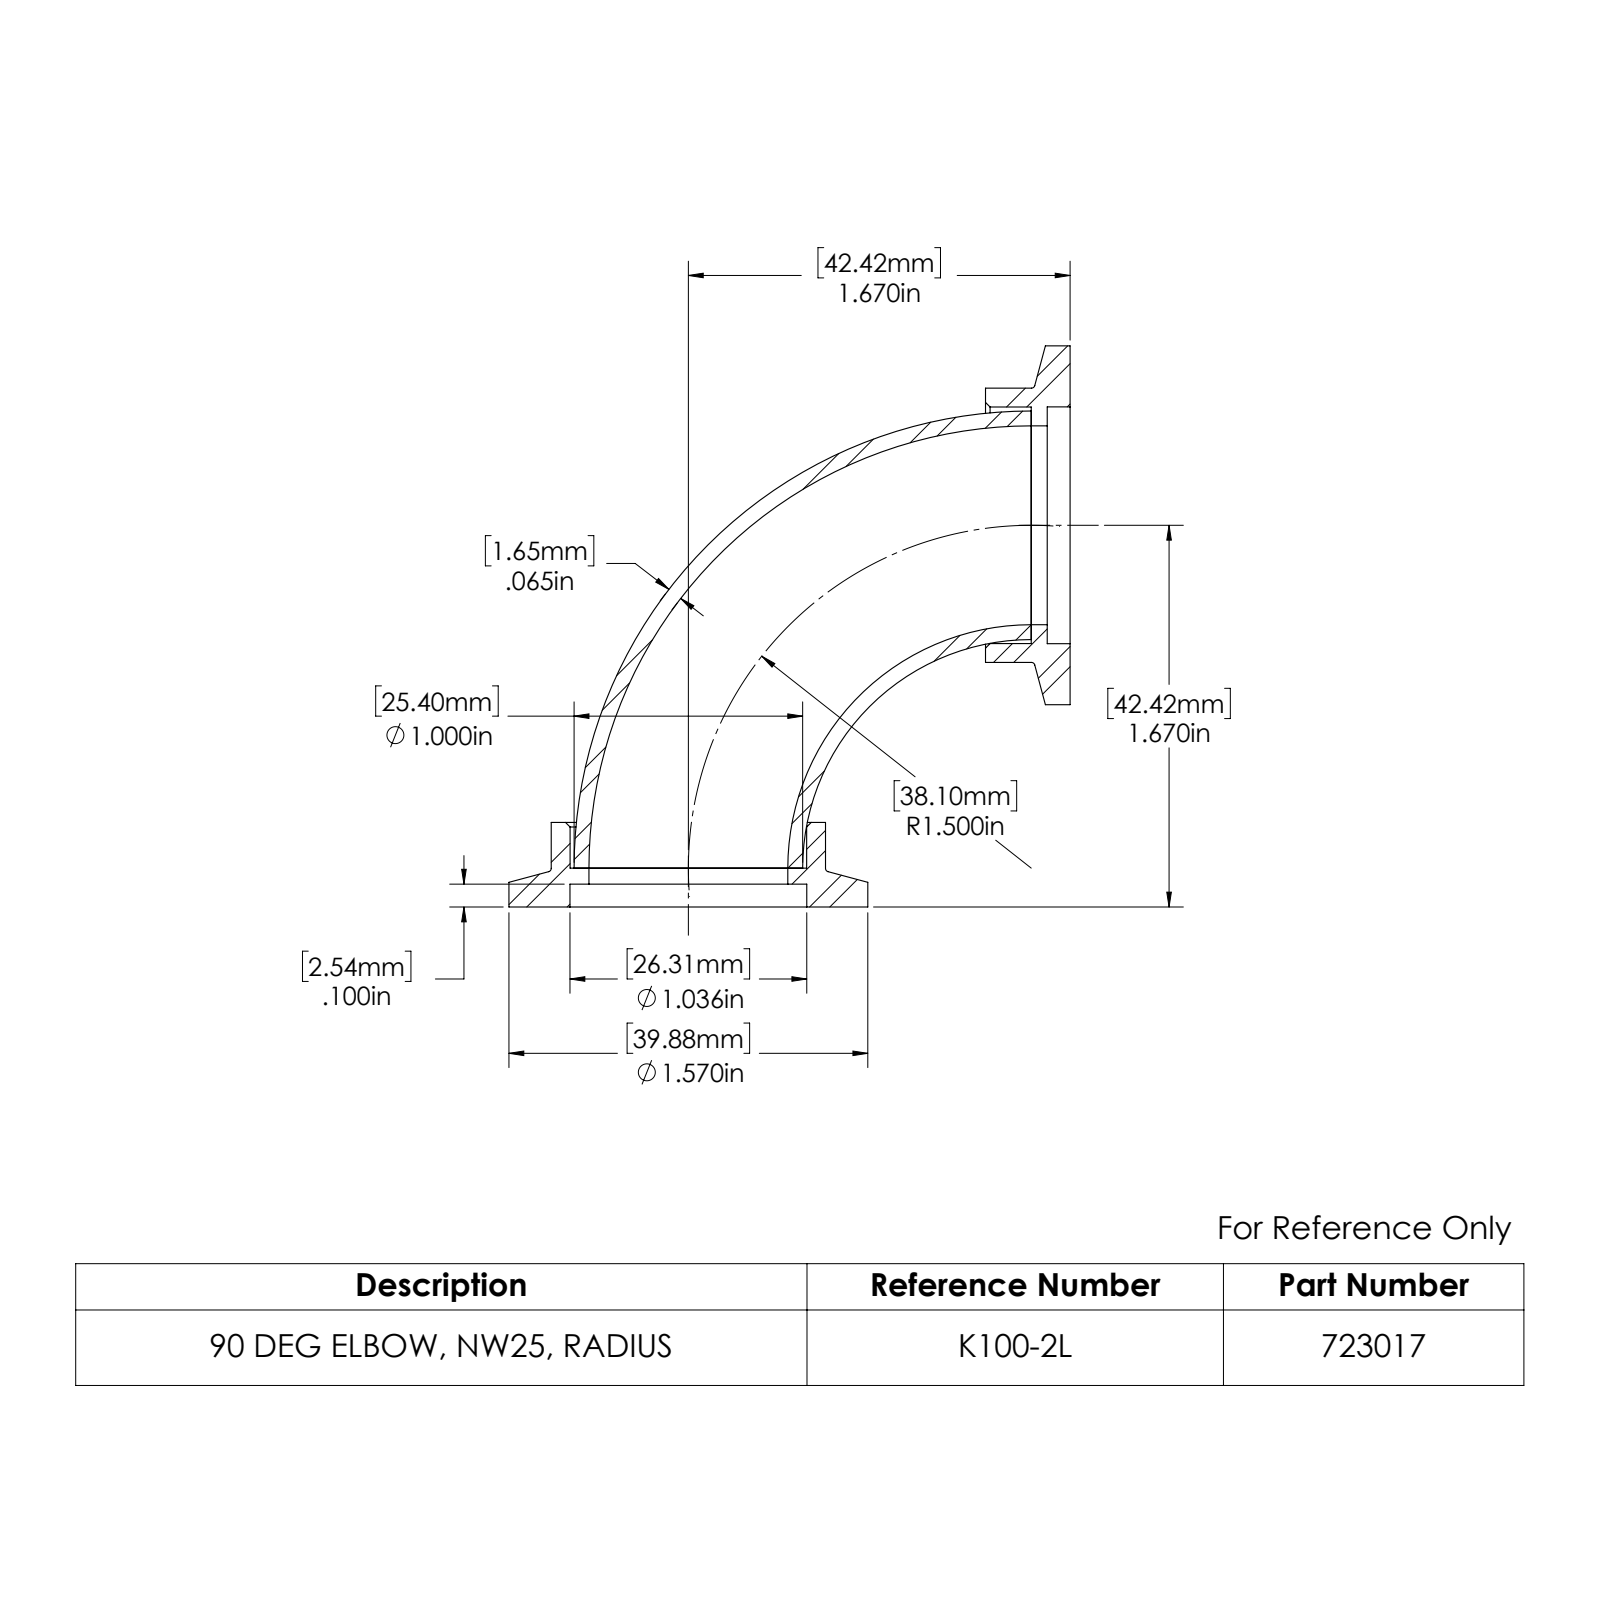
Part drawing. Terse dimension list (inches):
name: 972301; 723017; 042197
written by: SolidWorks 2022 (AUTOMOTIVE_DESIGN)
unit: in
bodies: 3 solids, 42 faces (10 planar, 20 cylindrical, 12 other)
size: 2.455 × 2.455 × 1.57
volume: 0.911 in³; area: 24.62 in²
holes: 2× ⌀0.87, 2× ⌀1.035, 2× ⌀1.036
bosses: 2× ⌀1.57, 2× ⌀1.2
face distances: 0.17, 0.37, 0.2, 0.1, 0.07, 0.27
